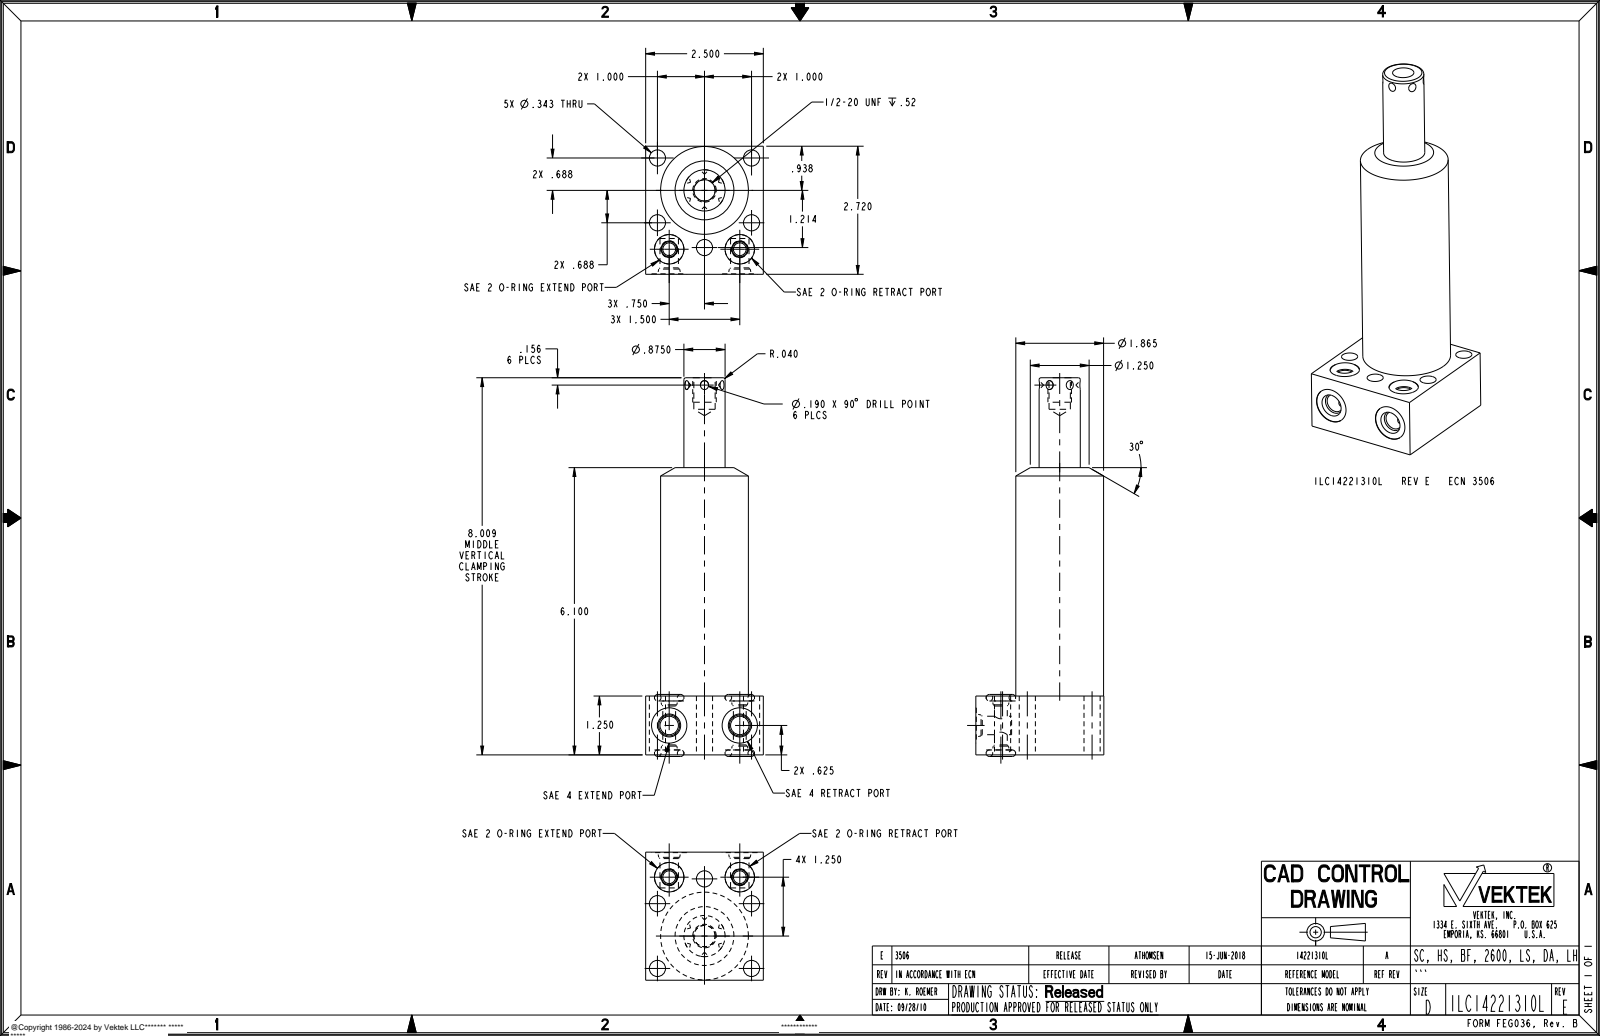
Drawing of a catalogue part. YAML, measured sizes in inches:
part_name: "ILC14221310L"
step_written_by: "PRO/ENGINEER BY PARAMETRIC TECHNOLOGY CORPORATION, 2013320 (AUTOMOTIVE_DESIGN)"
units: inches
bodies: {solids: 5, faces: 117, planar: 17, cylindrical: 42, other: 58}
overall_size: [8.043, 2.72, 2.5]
volume: 21.73
surface_area: 73.18
round_holes:
  - {diameter: 0.343, count: 5}
  - {diameter: 0.272, count: 2}
  - {diameter: 0.392, count: 2}
  - {diameter: 0.625, count: 2}
  - {diameter: 0.75, count: 2}
  - {diameter: 0.453, count: 1}
round_bosses_or_shafts:
  - {diameter: 1.865, count: 1}
  - {diameter: 0.875, count: 1}
  - {diameter: 0.5, count: 1}
face_to_face_distances: [2.5, 1.25, 2.72, 0.105, 1.145, 6.1, 4.85, 2.71, 1.04, 5.995]
hole_center_spacings: [1.214, 0.615, 0.751, 1.13, 1.376, 1.458, 1.5, 1.838]
